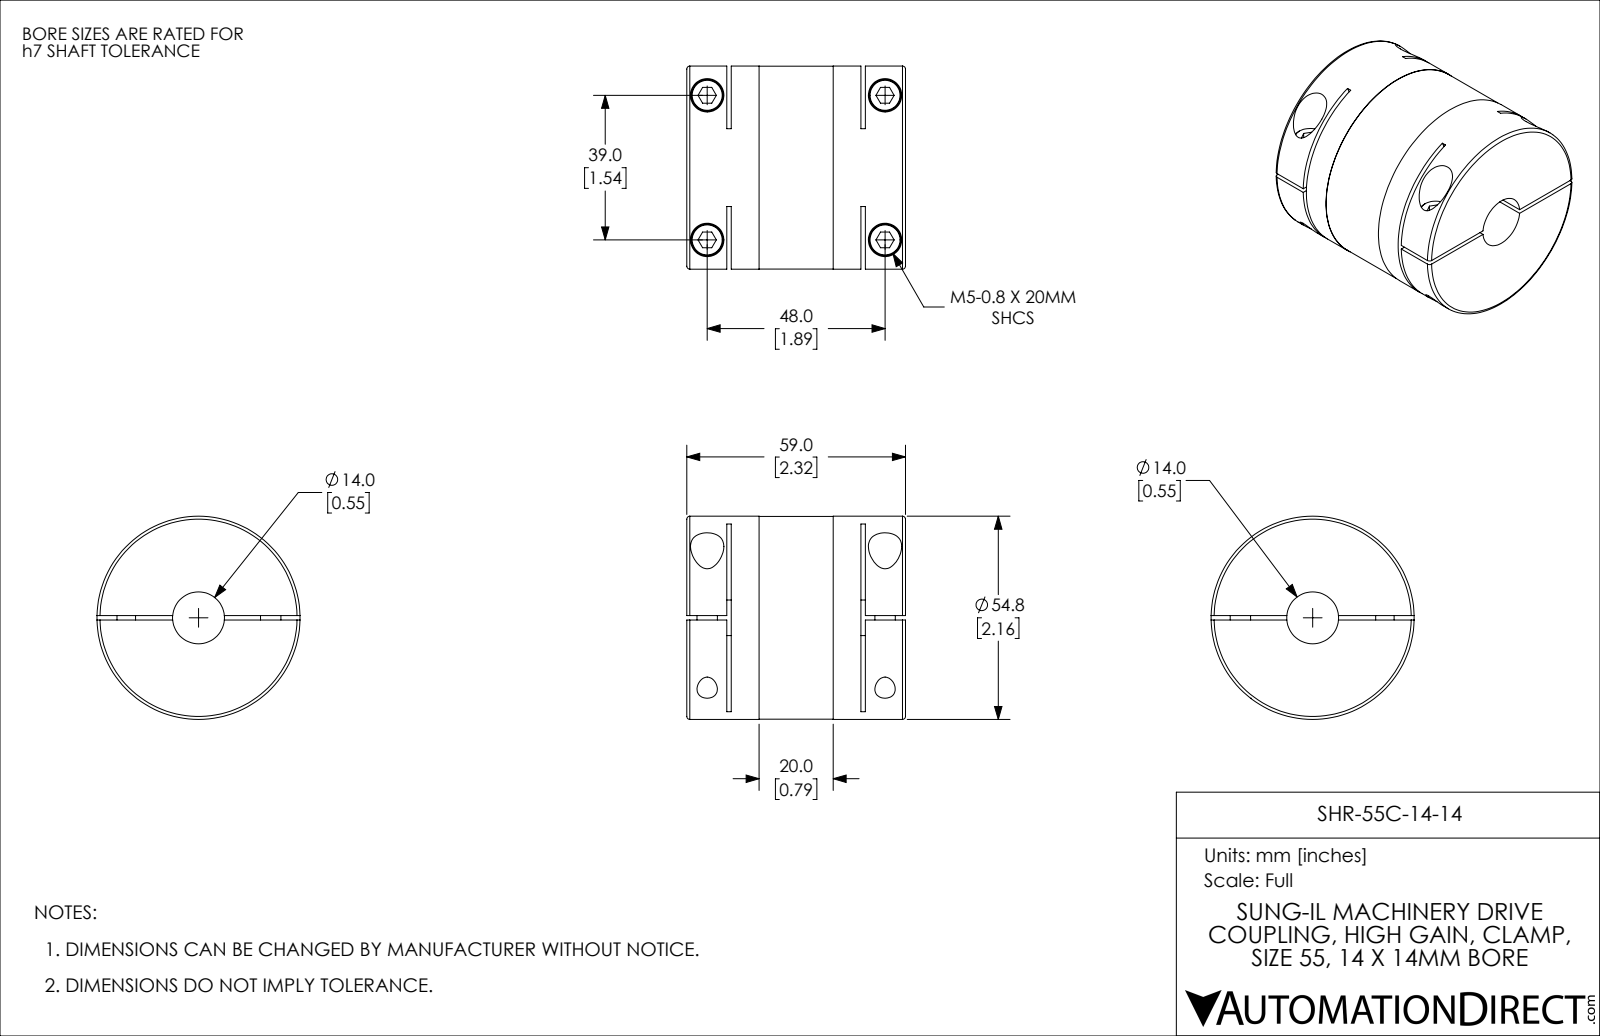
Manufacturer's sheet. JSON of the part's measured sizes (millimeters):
{"part_name": "SHR-55C-14-14", "step_written_by": "SolidWorks 2021 (CONFIG_CONTROL_DESIGN)", "units": "millimeters", "bodies": {"solids": 1, "faces": 144, "planar": 70, "cylindrical": 58, "other": 16}, "overall_size": [59, 54.8, 54.8], "volume_mm3": 121332, "surface_area_mm2": 28321, "round_holes": [[5.5, 4], [9, 4], [14, 1], [16, 1]], "round_bosses_or_shafts": [[8.5, 4], [5, 2], [54.8, 1], [54.7, 1]], "partial_cylinders_radius": [[60, 2]], "face_to_face_distances": [1.2, 12, 47, 10.8, 48.2, 36.2, 59, 35, 37.4, 19.5], "hole_center_spacings": [39, 48, 61.85]}
